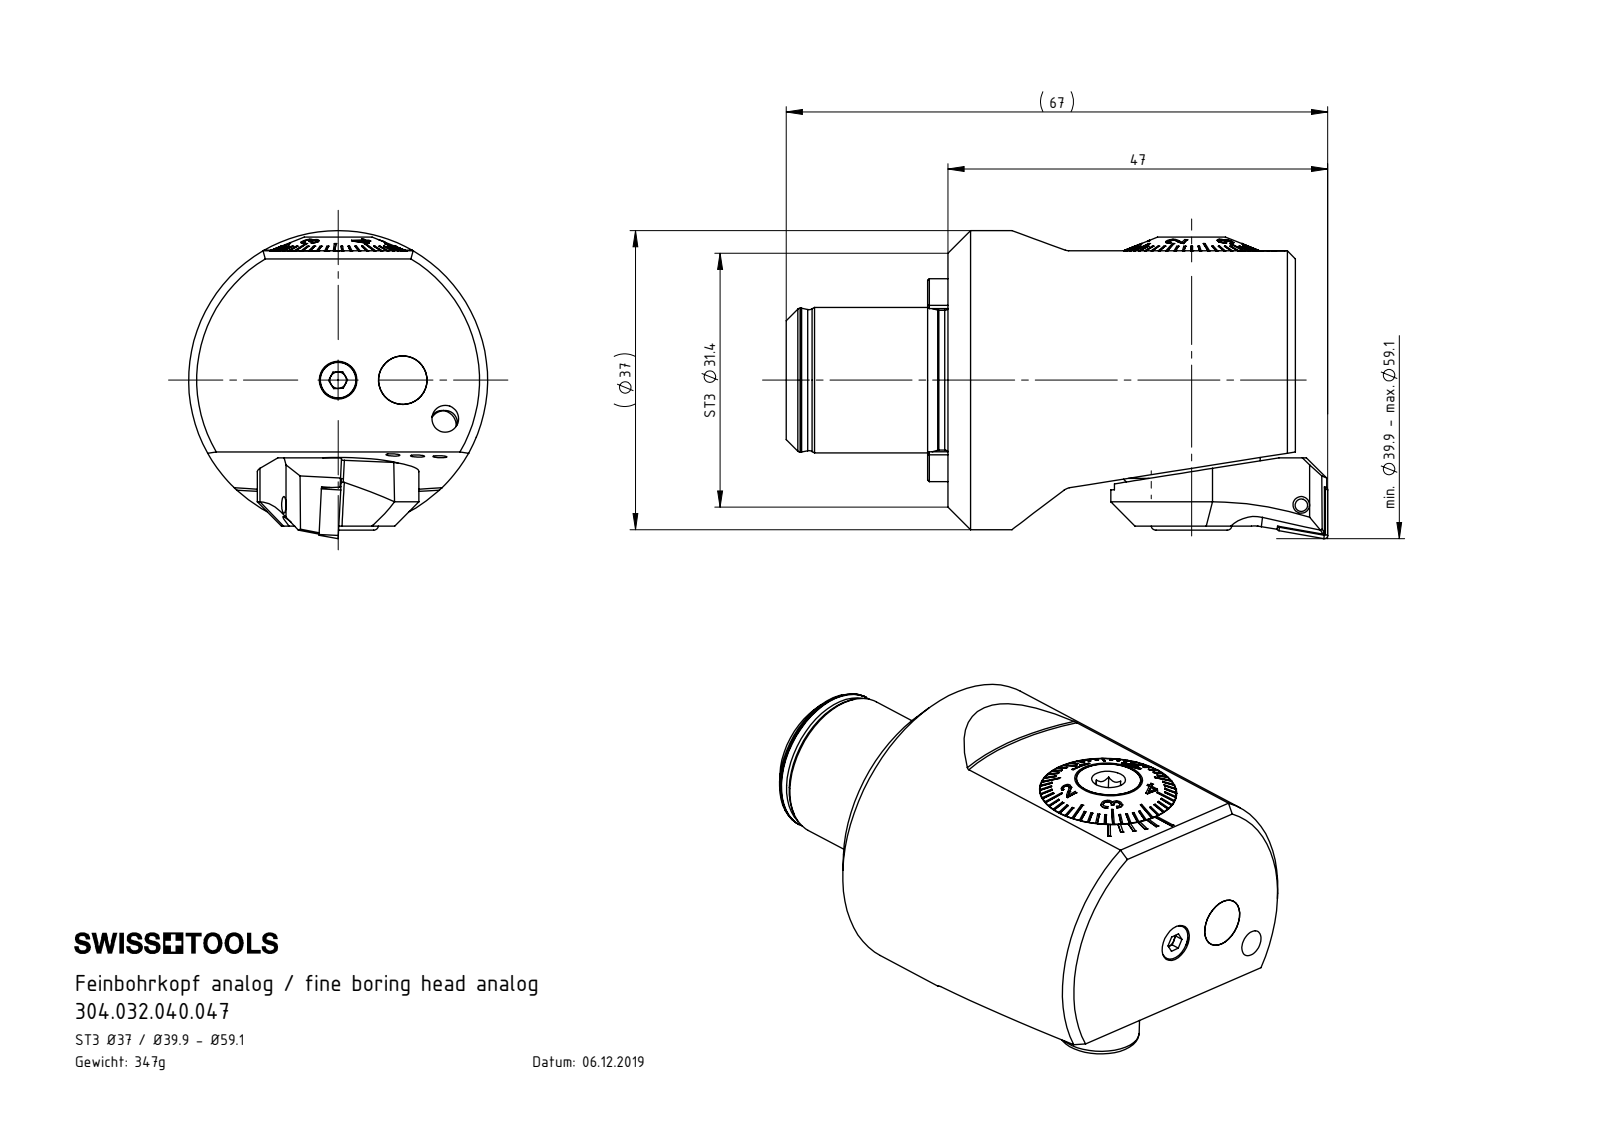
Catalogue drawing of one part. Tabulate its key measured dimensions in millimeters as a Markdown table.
| quantity | value |
| --- | --- |
| part name | F32-BG2.014.012_A; T7 M2.5 x 6; DIN 3771 - 15x1.0; F32-BG2.017.004_A (+8 more) |
| STEP written by | SolidWorks 2017 (CONFIG_CONTROL_DESIGN) |
| units | millimeters |
| bodies | 15 solids, 724 faces (306 planar, 134 cylindrical, 284 other) |
| overall size | 63 × 37.05 × 37 |
| volume | 43 324 mm³ |
| surface area | 17 201 mm² |
| round holes (diameter × count) | 1.5 × 3, 3.3 × 3, 2.8 × 2, 5 × 2, 2.05 × 1, 2.7 × 1, 2.9 × 1, 3 × 1, 4.2 × 1, 6 × 1, 6.8 × 1, 7 × 1 |
| round bosses / shafts (diameter × count) | 6 × 2, 37 × 1, 18 × 1, 17.8 × 1, 17.3 × 1, 17 × 1, 16.98 × 1, 16.85 × 1 |
| partial cylindrical surfaces (radius × count) | 0.5 × 7, 1.4 × 4, 1.75 × 2, 2 × 2, 2.73 × 2, 9.05 × 2, 3.2 × 1 |
| main face-to-face distances | 43, 4.5, 0.8, 3.7, 1.5, 24.05, 2.2, 2.3, 28.55, 26.25 |
| hole center spacings | 10.85, 13.48, 8, 8.72, 21.7, 37.9, 45.07 |
